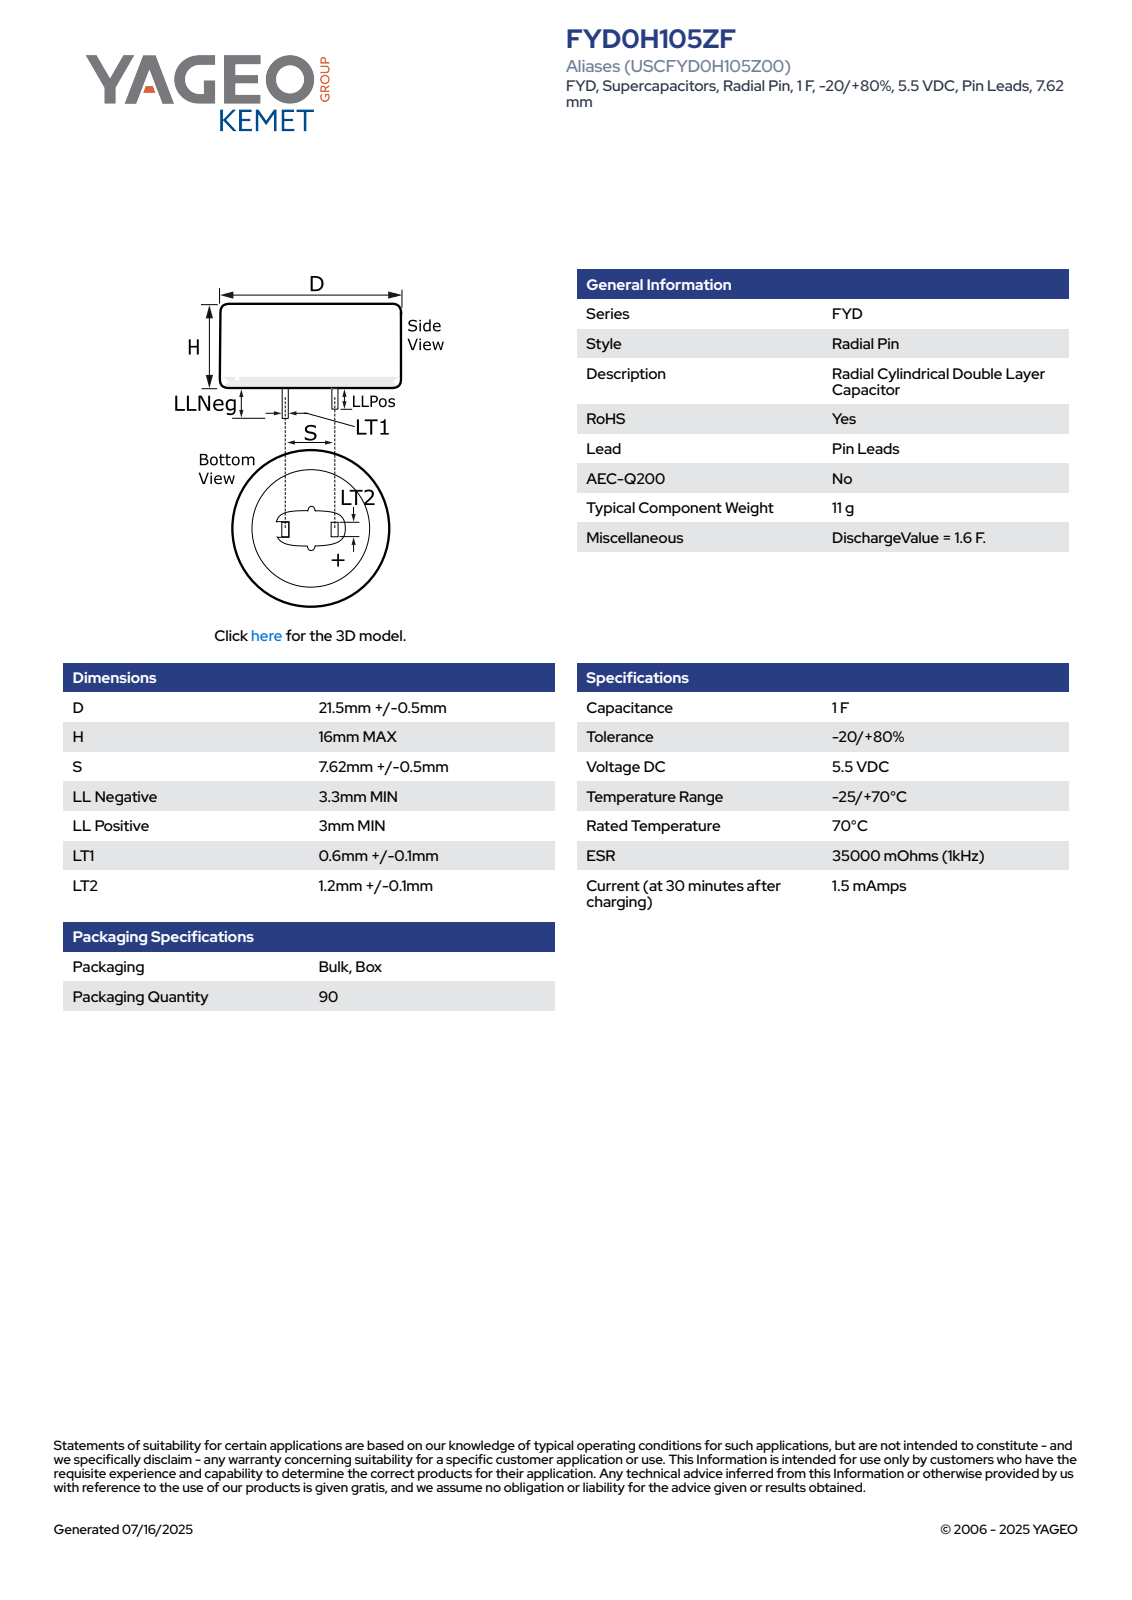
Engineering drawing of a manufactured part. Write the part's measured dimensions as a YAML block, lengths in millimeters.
part_name: "CDR_LPLLN_D22L16S7.62LLNEG3.3LLPOS3LT10.7LT21.3"
step_written_by: "SolidWorks 2014 (AUTOMOTIVE_DESIGN)"
units: millimeters
bodies: {solids: 1, faces: 78, planar: 70, cylindrical: 4, other: 4}
overall_size: [22, 22, 19.3]
volume: 6057
surface_area: 1830
round_bosses_or_shafts:
  - {diameter: 22, count: 1}
partial_cylinders:
  - {radius: 11.01, count: 1}
face_to_face_distances: [16, 15.99, 0.7, 7.62, 1.3, 8.32, 6.92, 3.3, 19.29, 19.3]
